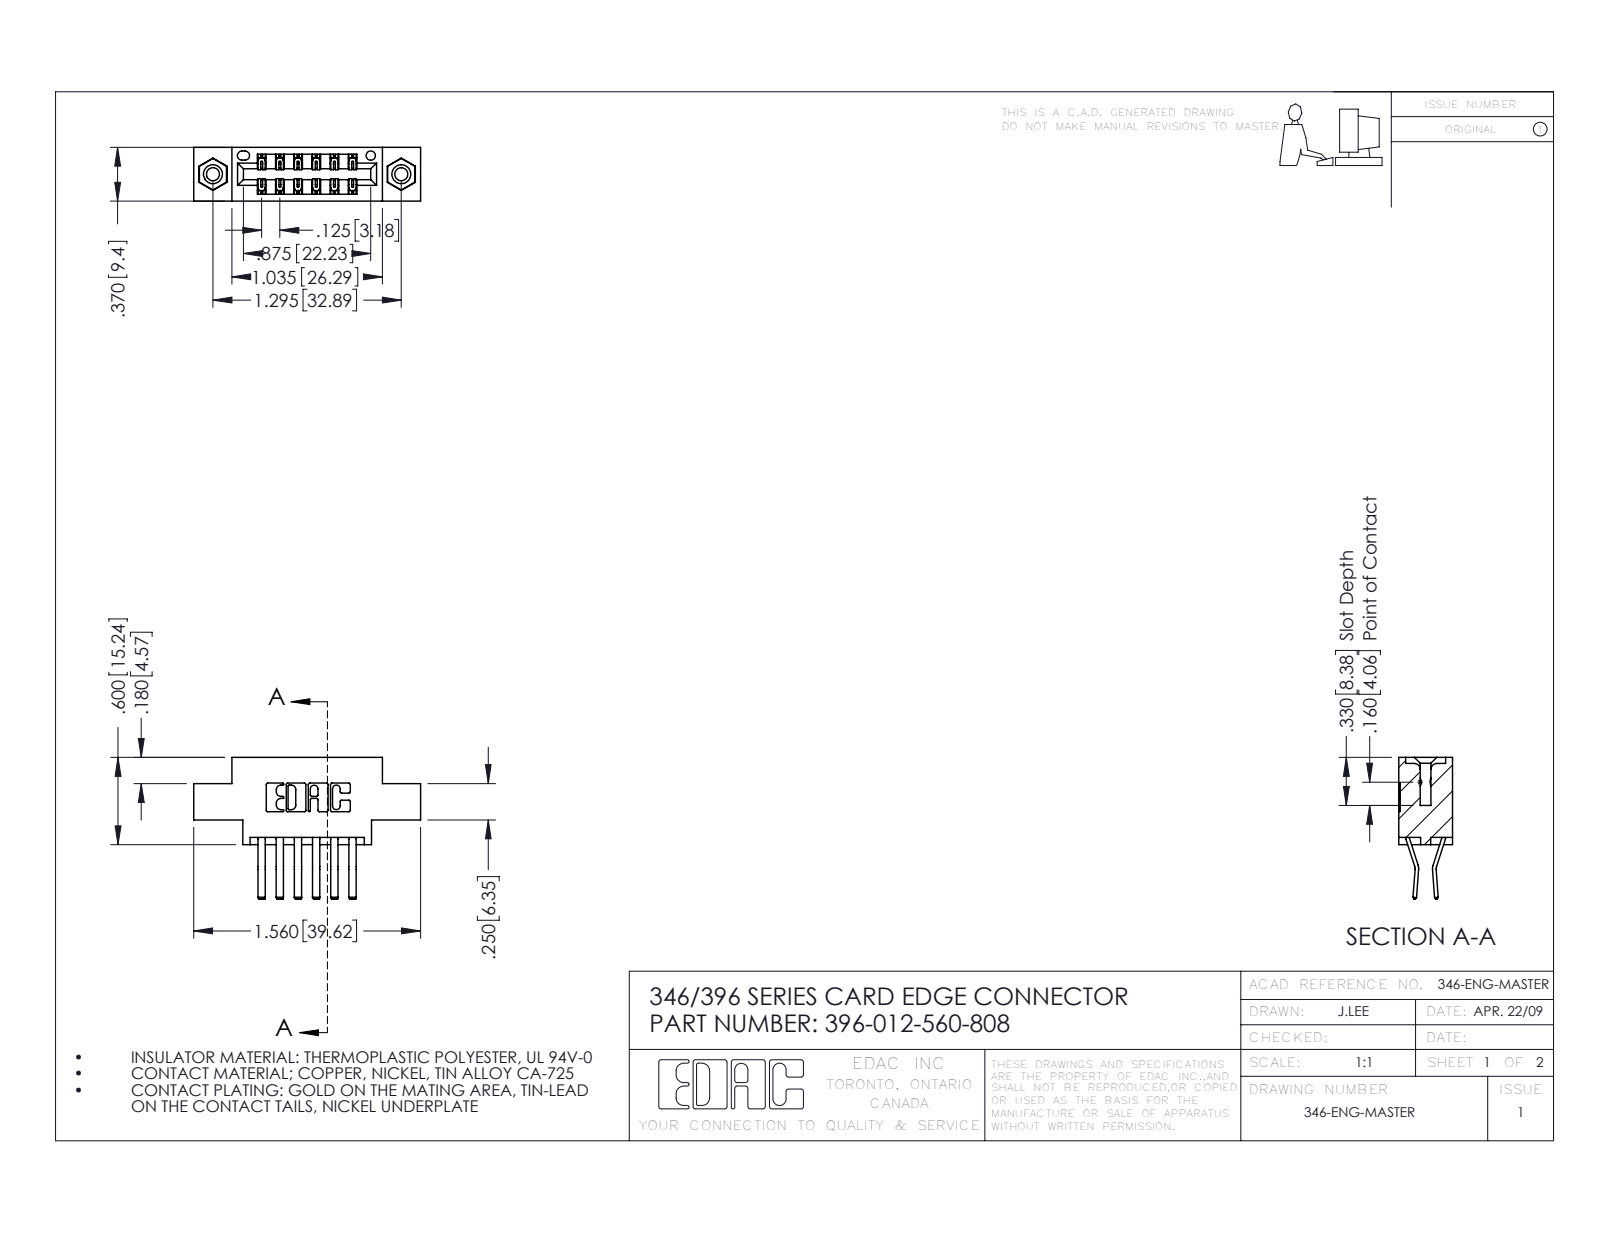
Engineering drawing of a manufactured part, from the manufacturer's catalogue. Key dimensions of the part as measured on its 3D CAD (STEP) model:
Part name (STEP PRODUCT): 345-292-001_560 Tail; 345-250-001_345-250-003-102; 396-012-560-808; 346 Part_0.170 Offset - 0.156 Dia-TI
STEP written by: SolidWorks 2016 (CONFIG_CONTROL_DESIGN)
Units: inches
Bodies: 15 solids, 834 faces (532 planar, 286 cylindrical, 16 other)
Overall size (bounding box): 1.56 × 0.975 × 0.37
Volume: 0.214 in³ · Surface area: 7.218 in²
Round holes (diameter × count): ⌀0.089 ×2, ⌀0.125 ×2, ⌀0.156 ×2, ⌀0.064 ×1
Round bosses / shafts (diameter × count): ⌀0.155 ×2
Partial cylindrical surfaces — rounded edges, fillets, slot ends (radius × count): R0.01 ×22, R0.006 ×18, R0.007 ×6, R0.031 ×6, R0.026 ×3, R0.01 ×2, R0.014 ×2, R0.022 ×2
Main face-to-face distances: 0.25, 0.37, 0.048, 0.322, 0.025, 0.222, 0.148, 0.1, 0.174, 0.072
Hole centre spacings: 0.246, 1.092, 1.295
